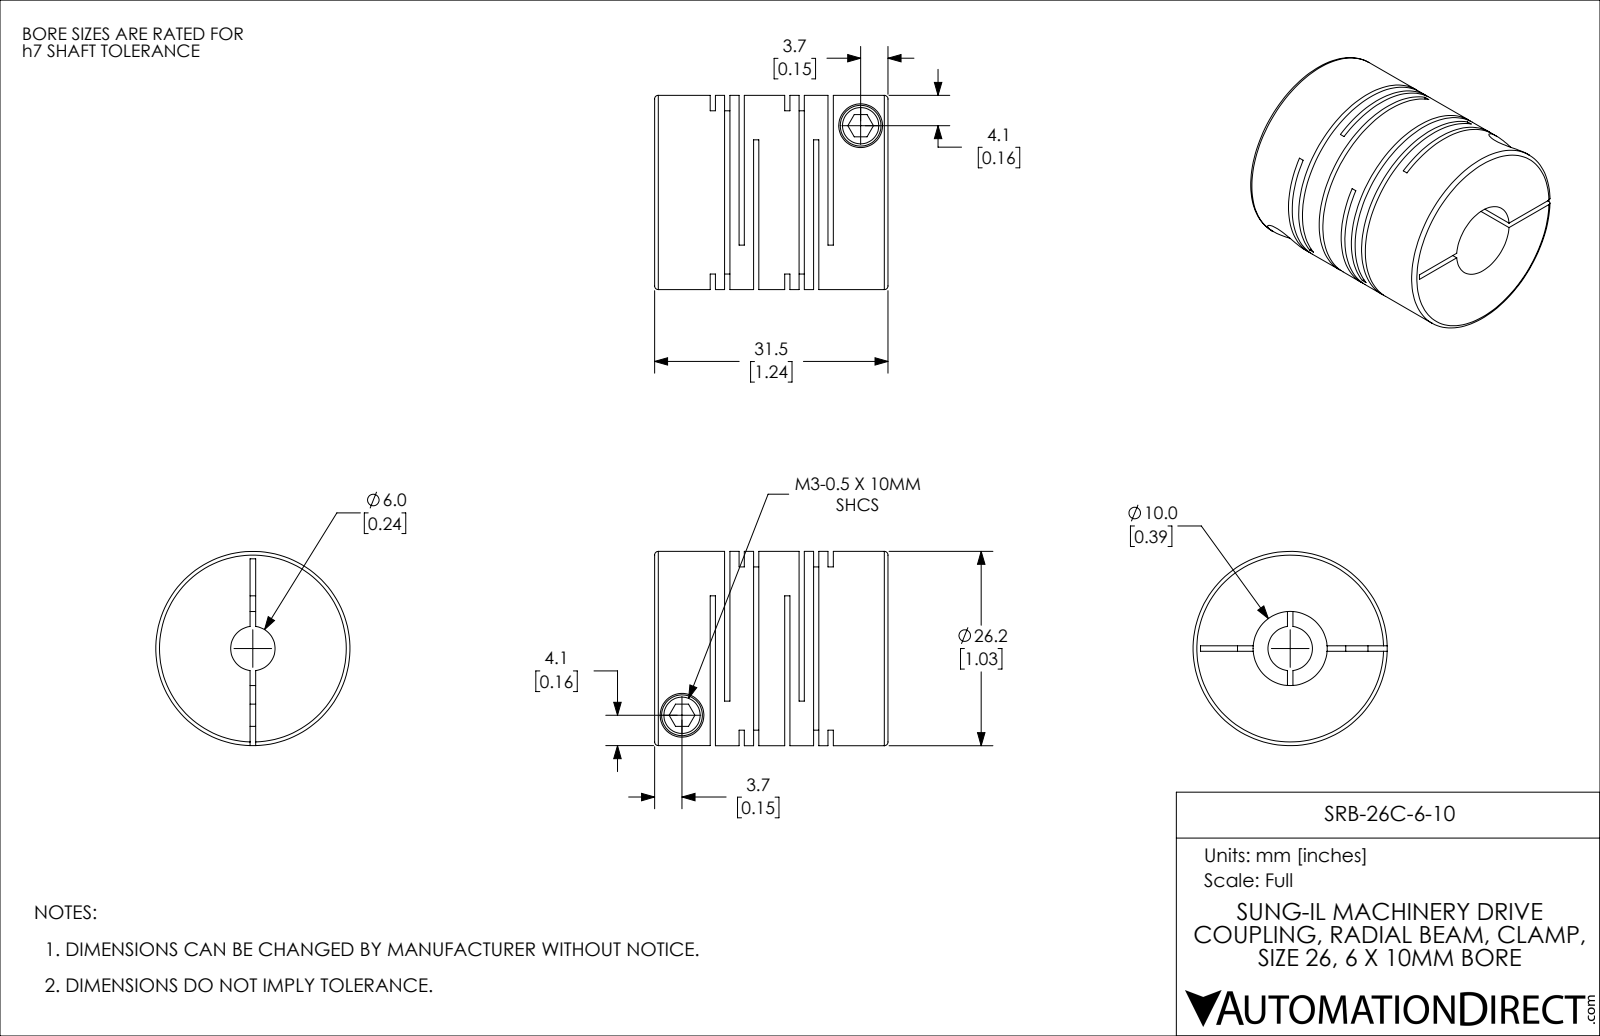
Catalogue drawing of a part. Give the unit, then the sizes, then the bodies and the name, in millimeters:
Units: millimetres
Overall size (bounding box): 31.5 × 26.2 × 26.2
Round holes (diameter × count): ⌀3 ×2, ⌀5.9 ×2, ⌀6 ×1, ⌀10 ×1
Round bosses / shafts (diameter × count): ⌀5.5 ×2, ⌀26.2 ×1
Main face-to-face distances: 1.95, 10.05, 0.71, 3.9, 8.1, 12, 1.24, 2.66, 9.34, 13.95
Volume: 12 297 mm³ · Surface area: 10 786 mm²
Bodies: 1 solid, 114 faces (60 planar, 42 cylindrical, 12 other)
Part name (STEP PRODUCT): SRB-26C-6-10
STEP written by: SolidWorks 2021 (CONFIG_CONTROL_DESIGN)
